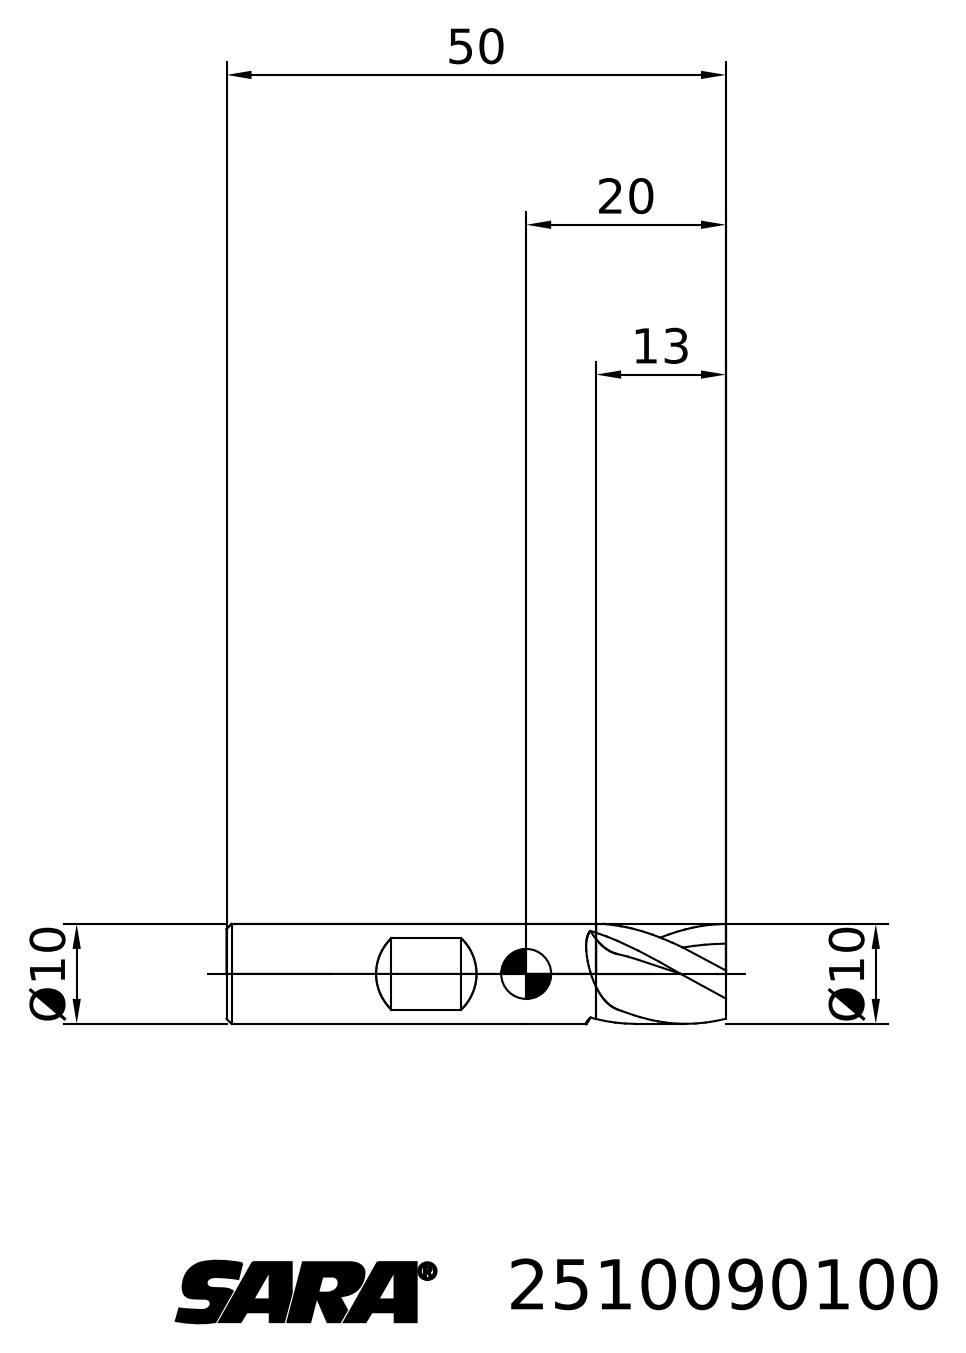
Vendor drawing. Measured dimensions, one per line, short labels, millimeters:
written by: TDM (AUTOMOTIVE_DESIGN)
unit: mm
bodies: 2 solids, 25 faces (7 planar, 0 cylindrical, 18 other)
size: 50 × 10 × 10
volume: 3 422 mm³; area: 1 841 mm²
face distances: 37, 13, 50
